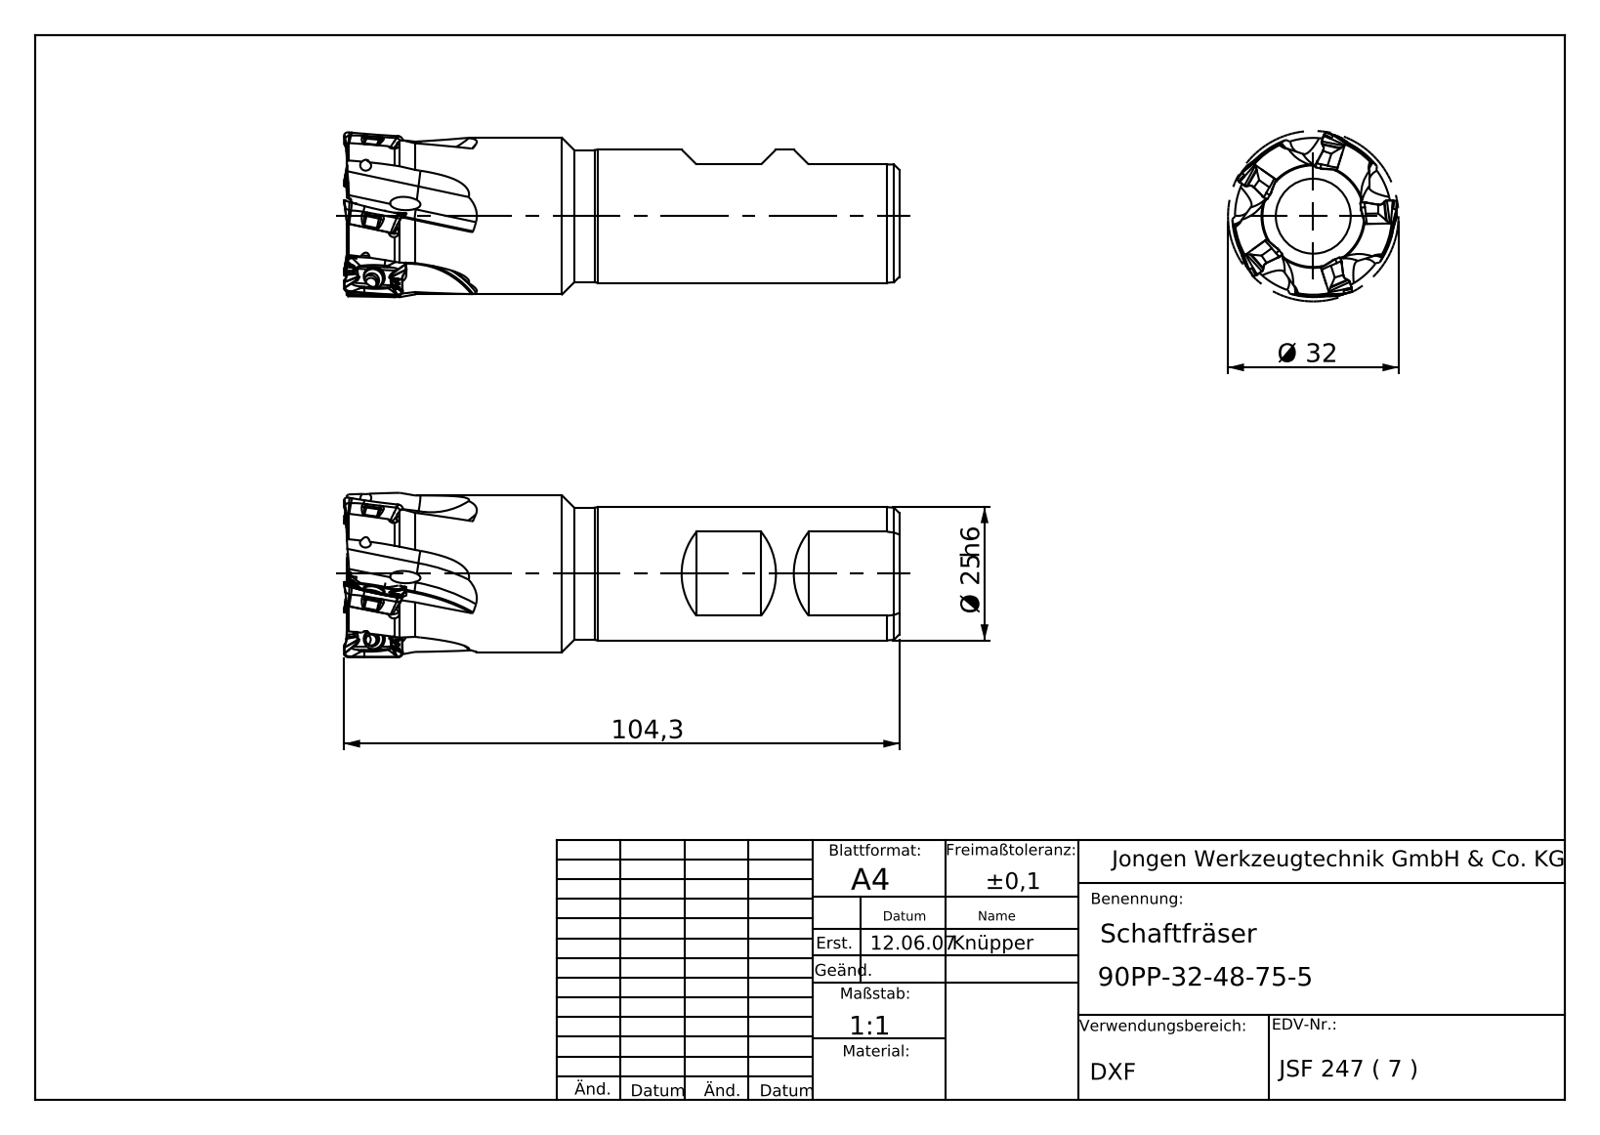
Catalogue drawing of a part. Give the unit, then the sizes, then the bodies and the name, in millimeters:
Units: millimetres
Overall size (bounding box): 104.3 × 32.04 × 32.04
Round holes (diameter × count): ⌀2.5 ×5, ⌀6.5 ×1
Round bosses / shafts (diameter × count): ⌀29.38 ×1, ⌀25 ×1, ⌀24.8 ×1
Partial cylindrical surfaces — rounded edges, fillets, slot ends (radius × count): R0.2 ×10, R1.5 ×5, R9.53 ×1
Main face-to-face distances: 102.32, 14.88, 11.31, 26.19, 0.5, 3.29, 3.28, 0.51, 0.49
Volume: 53 966 mm³ · Surface area: 13 243 mm²
Bodies: 1 solid, 174 faces (53 planar, 39 cylindrical, 82 other)
Part name (STEP PRODUCT): 90PP-32-48-75-5
STEP written by: SolidWorks 2012 (AUTOMOTIVE_DESIGN)
